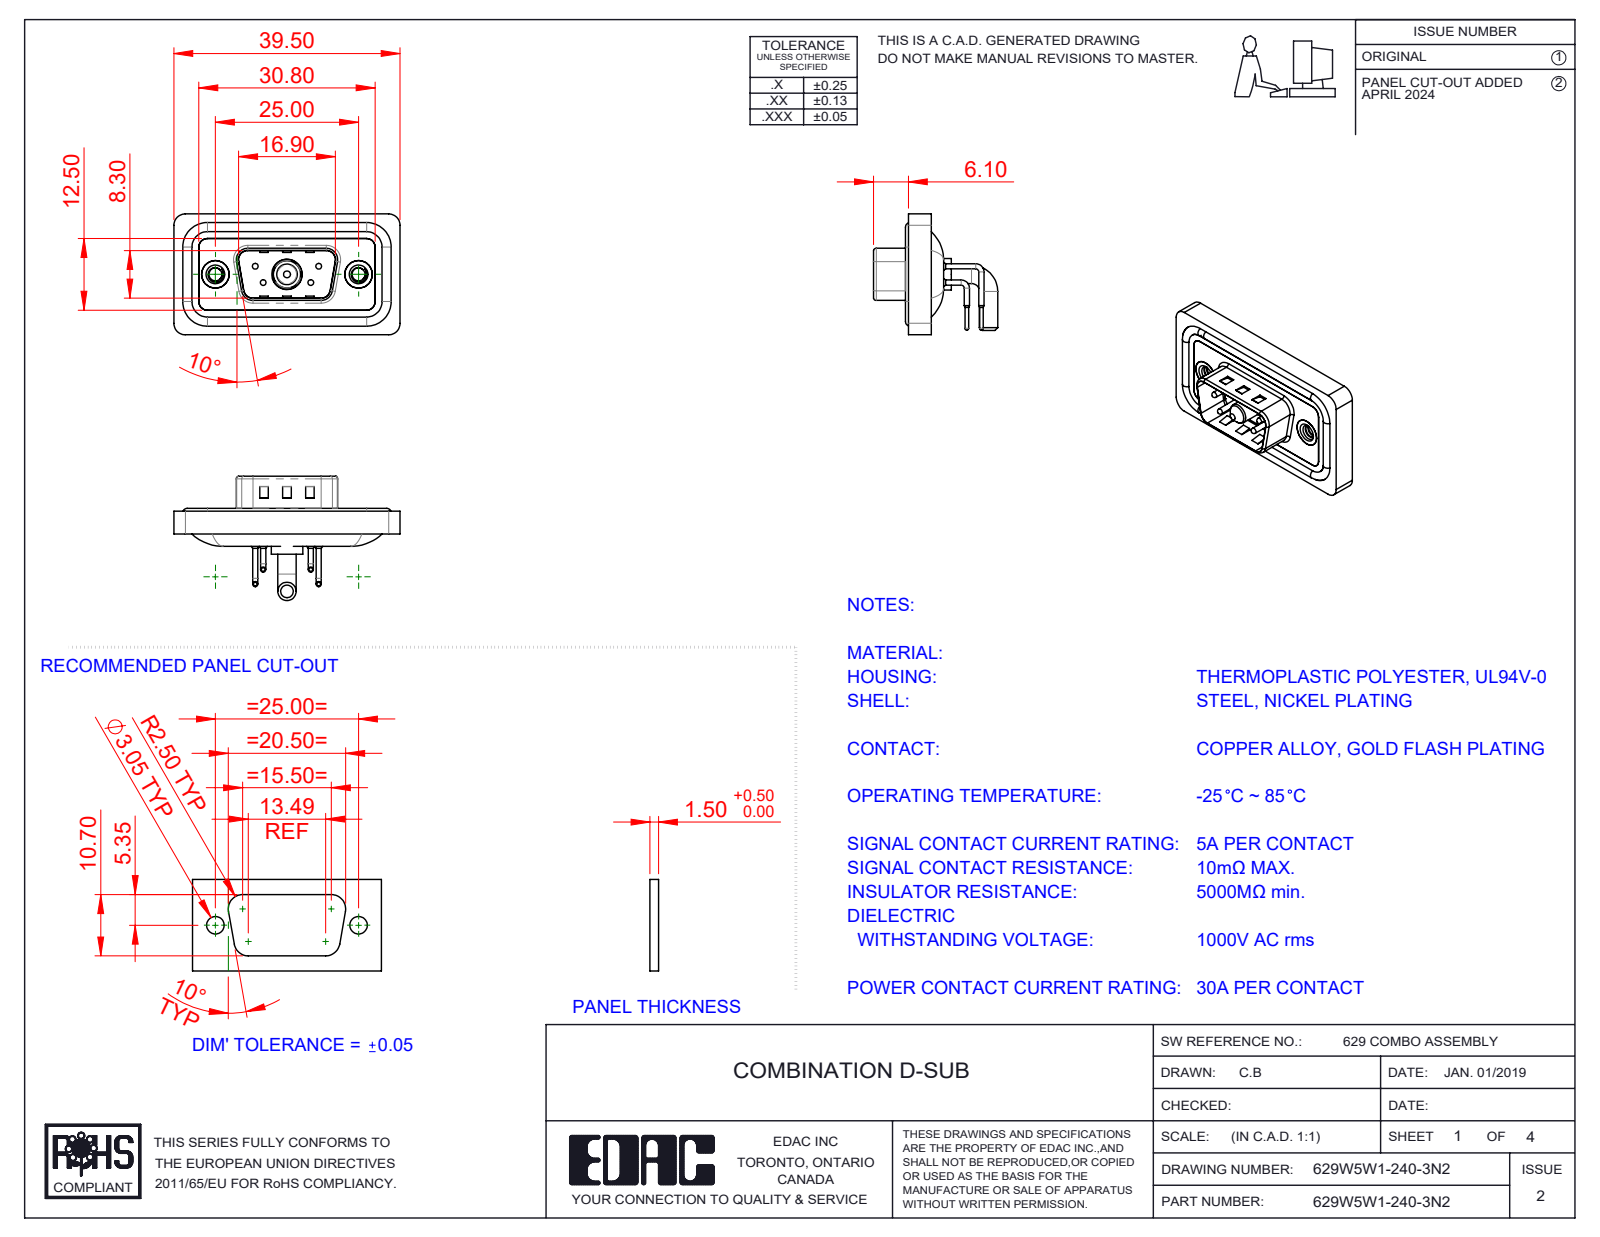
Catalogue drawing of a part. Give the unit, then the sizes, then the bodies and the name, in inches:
Units: inches
Overall size (bounding box): 1.555 × 0.854 × 0.831
Round holes (diameter × count): ⌀0.03 ×4, ⌀0.063 ×4, ⌀0.079 ×4, ⌀0.089 ×2, ⌀0.157 ×2, ⌀0.189 ×2, ⌀0.197 ×2, ⌀0.191 ×1, ⌀0.209 ×1
Round bosses / shafts (diameter × count): ⌀0.035 ×8, ⌀0.063 ×4, ⌀0.059 ×4, ⌀0.039 ×4, ⌀0.026 ×4, ⌀0.193 ×2, ⌀0.126 ×2, ⌀0.217 ×1
Partial cylindrical surfaces — rounded edges, fillets, slot ends (radius × count): R0.059 ×18, R0.079 ×18, R0.02 ×8, R0.063 ×8, R0.01 ×4, R0.024 ×4, R0.026 ×4, R0.035 ×4
Main face-to-face distances: 0.016, 0.114, 0.043, 0.031, 0.083, 0.098, 0.063, 0.122, 0.177, 0.059
Hole centre spacings: 0.124, 0.225, 0.28, 0.492, 0.713, 0.173, 0.173, 0.327
Volume: 0.276 in³ · Surface area: 11.13 in²
Bodies: 13 solids, 894 faces (411 planar, 345 cylindrical, 138 other)
Part name (STEP PRODUCT): 629Combo Contact Row 1; 629W5W1-240-3N2; 629Combo Shell Rear_09 Contacts; 629Combo Shell Front_09 Contacts (+5 more)
STEP written by: SolidWorks 2023 (CONFIG_CONTROL_DESIGN)
